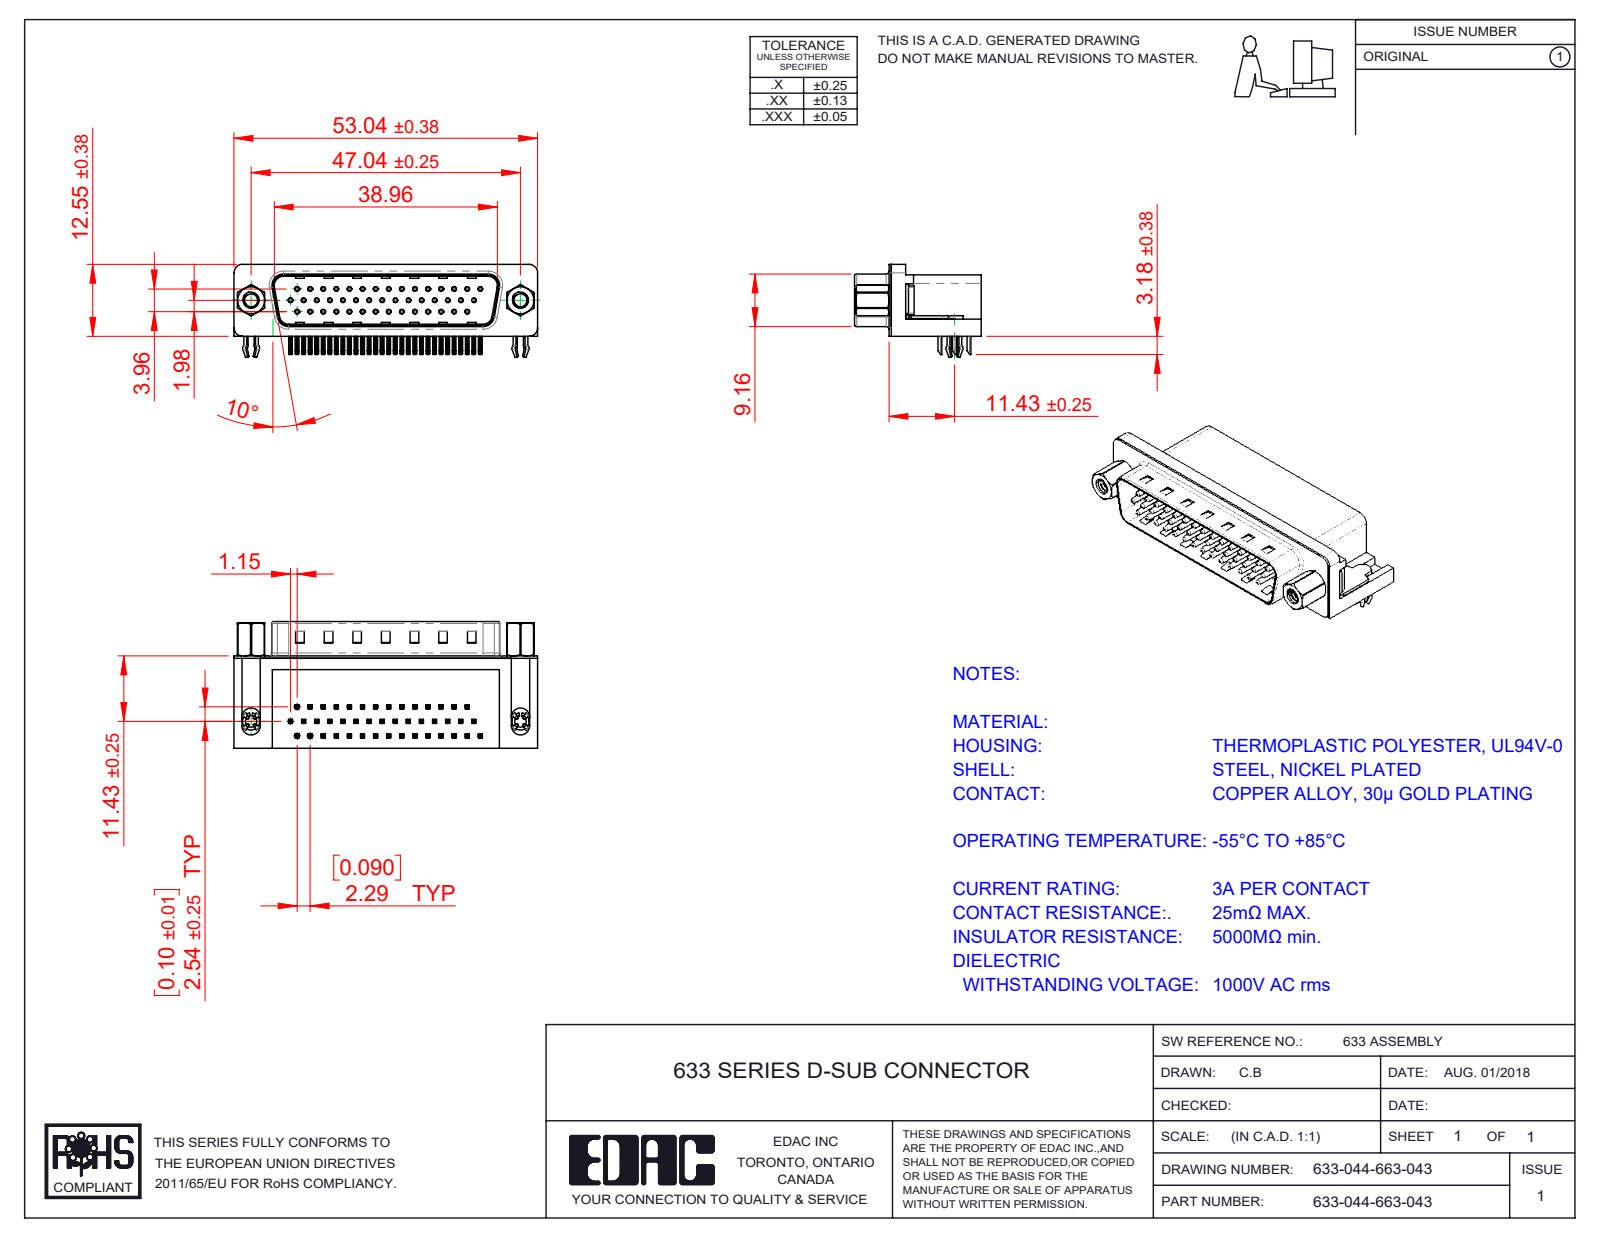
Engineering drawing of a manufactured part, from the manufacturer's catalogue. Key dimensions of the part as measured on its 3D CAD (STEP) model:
Part name (STEP PRODUCT): 633 4 Prong Board Lock; 633 4-40 Hex Standoff; 633 4-40 Threaded Rivet; 633 Housing_44 Contact (+5 more)
STEP written by: SolidWorks 2016 (CONFIG_CONTROL_DESIGN)
Units: millimetres
Bodies: 52 solids, 3930 faces (2381 planar, 1130 cylindrical, 419 other)
Overall size (bounding box): 53.04 × 22.1 × 16.25
Volume: 8 326 mm³ · Surface area: 10 746 mm²
Round holes (diameter × count): ⌀0.35 ×44, ⌀0.8 ×44, ⌀2 ×2, ⌀2.26 ×2, ⌀2.29 ×2, ⌀4 ×2, ⌀4.8 ×2, ⌀5 ×2
Round bosses / shafts (diameter × count): ⌀0.75 ×44, ⌀4.9 ×2, ⌀4.75 ×2, ⌀3.9 ×2, ⌀3 ×2, ⌀2.79 ×2
Partial cylindrical surfaces — rounded edges, fillets, slot ends (radius × count): R0.25 ×188, R0.12 ×88, R1 ×16, R0.5 ×9, R1.6 ×8, R1.5 ×7, R0.9 ×4, R2 ×4
Main face-to-face distances: 0.4, 10.35, 15.7, 8.76, 2.9, 2.5, 16.1, 2.1, 10.7, 2.54
Hole centre spacings: 2.29, 4.57, 4.58, 2.28, 6.87, 9.16, 11.45, 2.27
